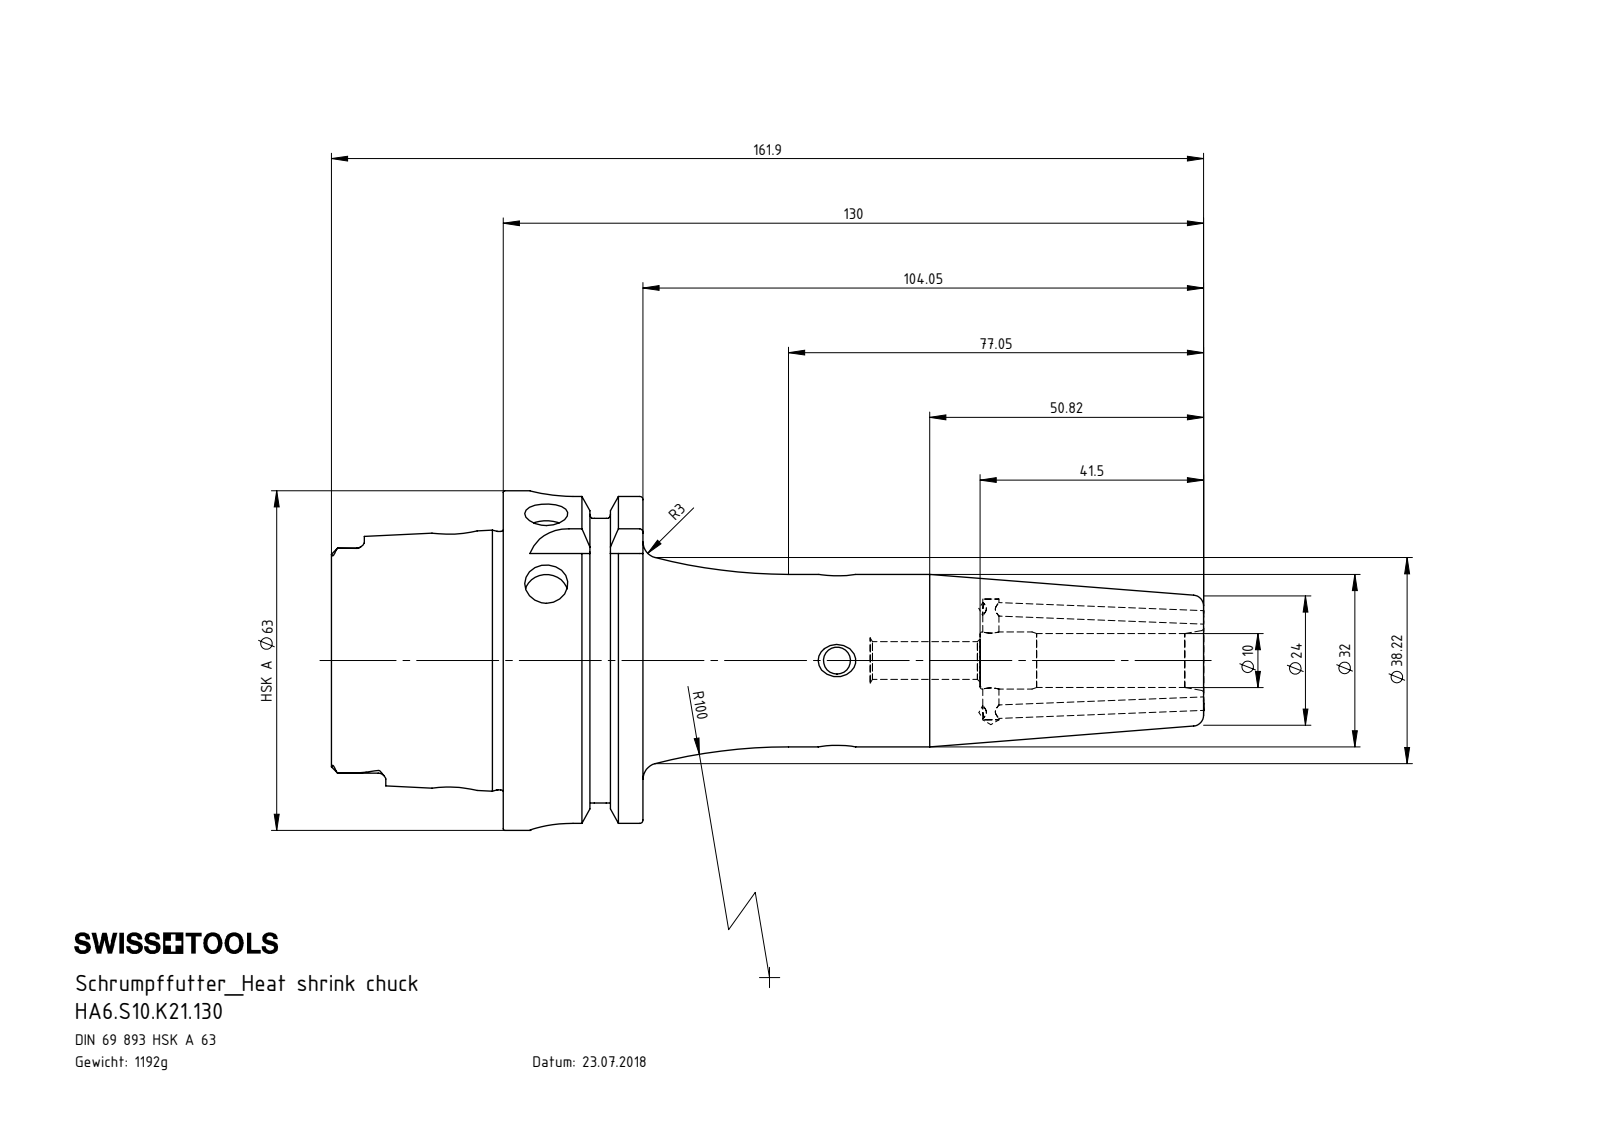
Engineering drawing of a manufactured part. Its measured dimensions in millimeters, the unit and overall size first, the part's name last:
Units: millimetres
Overall size (bounding box): 161.98 × 63 × 63
Round holes (diameter × count): ⌀2.5 ×2, ⌀5 ×2, ⌀8 ×2, ⌀10 ×2, ⌀3 ×1, ⌀4 ×1, ⌀7 ×1, ⌀7.5 ×1, ⌀8.4 ×1, ⌀10.6 ×1, ⌀17 ×1, ⌀19 ×1
Round bosses / shafts (diameter × count): ⌀3 ×2, ⌀63 ×1, ⌀54.95 ×1, ⌀47.94 ×1, ⌀32 ×1, ⌀8 ×1
Partial cylindrical surfaces — rounded edges, fillets, slot ends (radius × count): R1.4 ×6, R2.88 ×4, R8 ×4
Main face-to-face distances: 25.95, 16, 9.95, 31.9, 41.85, 57.85, 52.8, 21.8, 11.85, 53.7
Hole centre spacings: 28.55, 54.95, 70.95, 99.5
Volume: 151 810 mm³ · Surface area: 36 697 mm²
Bodies: 4 solids, 311 faces (101 planar, 85 cylindrical, 125 other)
Part name (STEP PRODUCT): HA6-S10.K21.130; ERU-AN3.K01.020_A; ERU-CJ2.001.006; HA6-S10.K21.130_C_Fertigbearbeitung
STEP written by: SolidWorks 2012 (CONFIG_CONTROL_DESIGN)
